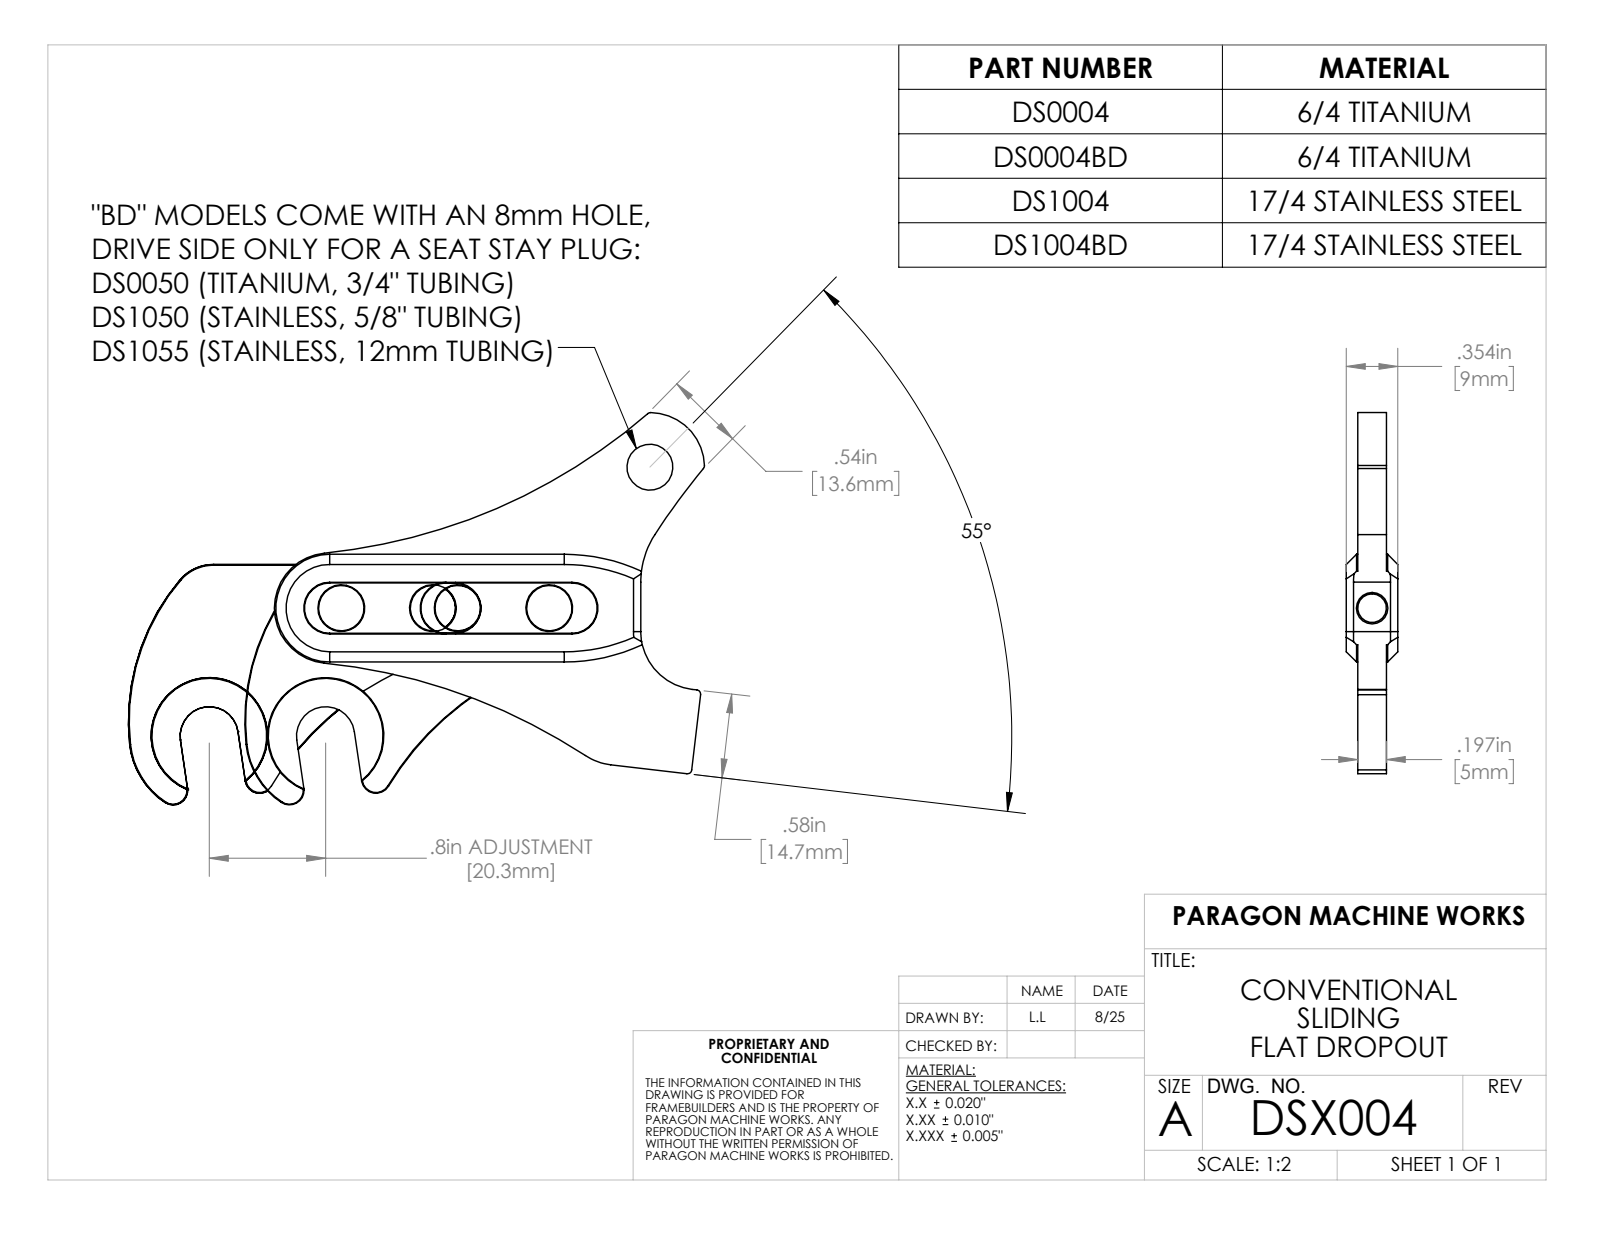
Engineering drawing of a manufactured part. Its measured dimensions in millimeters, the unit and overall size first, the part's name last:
Units: millimetres
Overall size (bounding box): 78.7 × 61 × 9
Round holes (diameter × count): ⌀5 ×1
Partial cylindrical surfaces — rounded edges, fillets, slot ends (radius × count): R0.8 ×4, R4.5 ×2, R10.2 ×2, R32.3 ×2, R101.6 ×2, R9.4 ×1, R9.5 ×1, R9.7 ×1
Main face-to-face distances: 5, 2, 7, 9, 9, 17.1, 13.9, 4.9, 4.9, 13.9
Volume: 12 000 mm³ · Surface area: 6 529 mm²
Bodies: 1 solid, 57 faces (20 planar, 27 cylindrical, 10 other)
Part name (STEP PRODUCT): DSX004
STEP written by: SolidWorks 2023 (AUTOMOTIVE_DESIGN)
